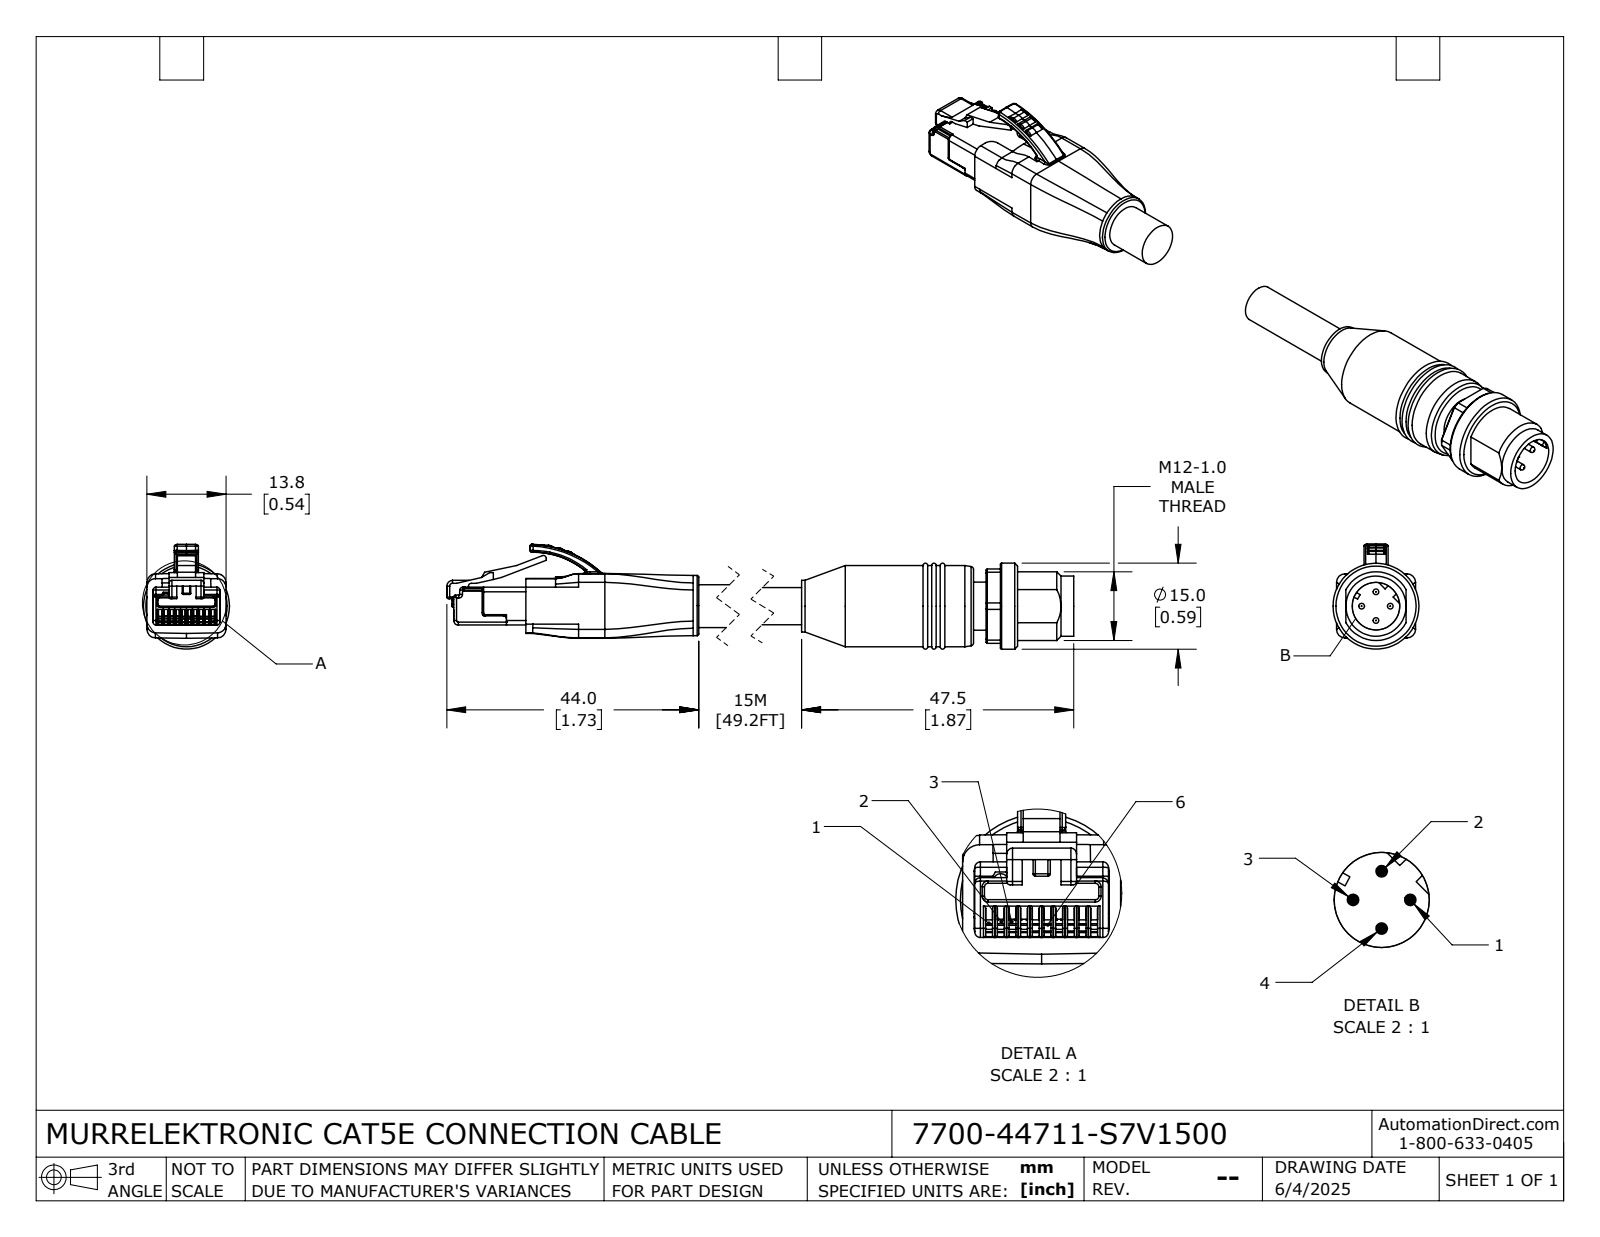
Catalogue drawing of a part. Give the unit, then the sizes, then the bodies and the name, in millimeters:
Units: millimetres
Overall size (bounding box): 144.5 × 18.29 × 15
Round holes (diameter × count): ⌀8.3 ×1
Round bosses / shafts (diameter × count): ⌀1 ×4, ⌀10.5 ×2, ⌀15 ×1, ⌀14.2 ×1, ⌀9 ×1, ⌀8.4 ×1, ⌀7.5 ×1, ⌀6.5 ×1
Partial cylindrical surfaces — rounded edges, fillets, slot ends (radius × count): R0.2 ×61, R0.5 ×25, R0.3 ×14, R1.5 ×9, R0.8 ×5, R0.54 ×2, R5 ×2, R0.13 ×1
Main face-to-face distances: 13.8, 2.2, 1.65, 12.15, 1.01, 12.79, 0.64, 11.14, 9.8, 0.9
Volume: 11 873 mm³ · Surface area: 5 775 mm²
Bodies: 2 solids, 757 faces (357 planar, 235 cylindrical, 165 other)
Part name (STEP PRODUCT): 7700-44711-S7V1500_MALE; 7700-44711-S7V1500_RJ45; 7700-44711-S7V1500
STEP written by: SolidWorks 2024 (CONFIG_CONTROL_DESIGN)
